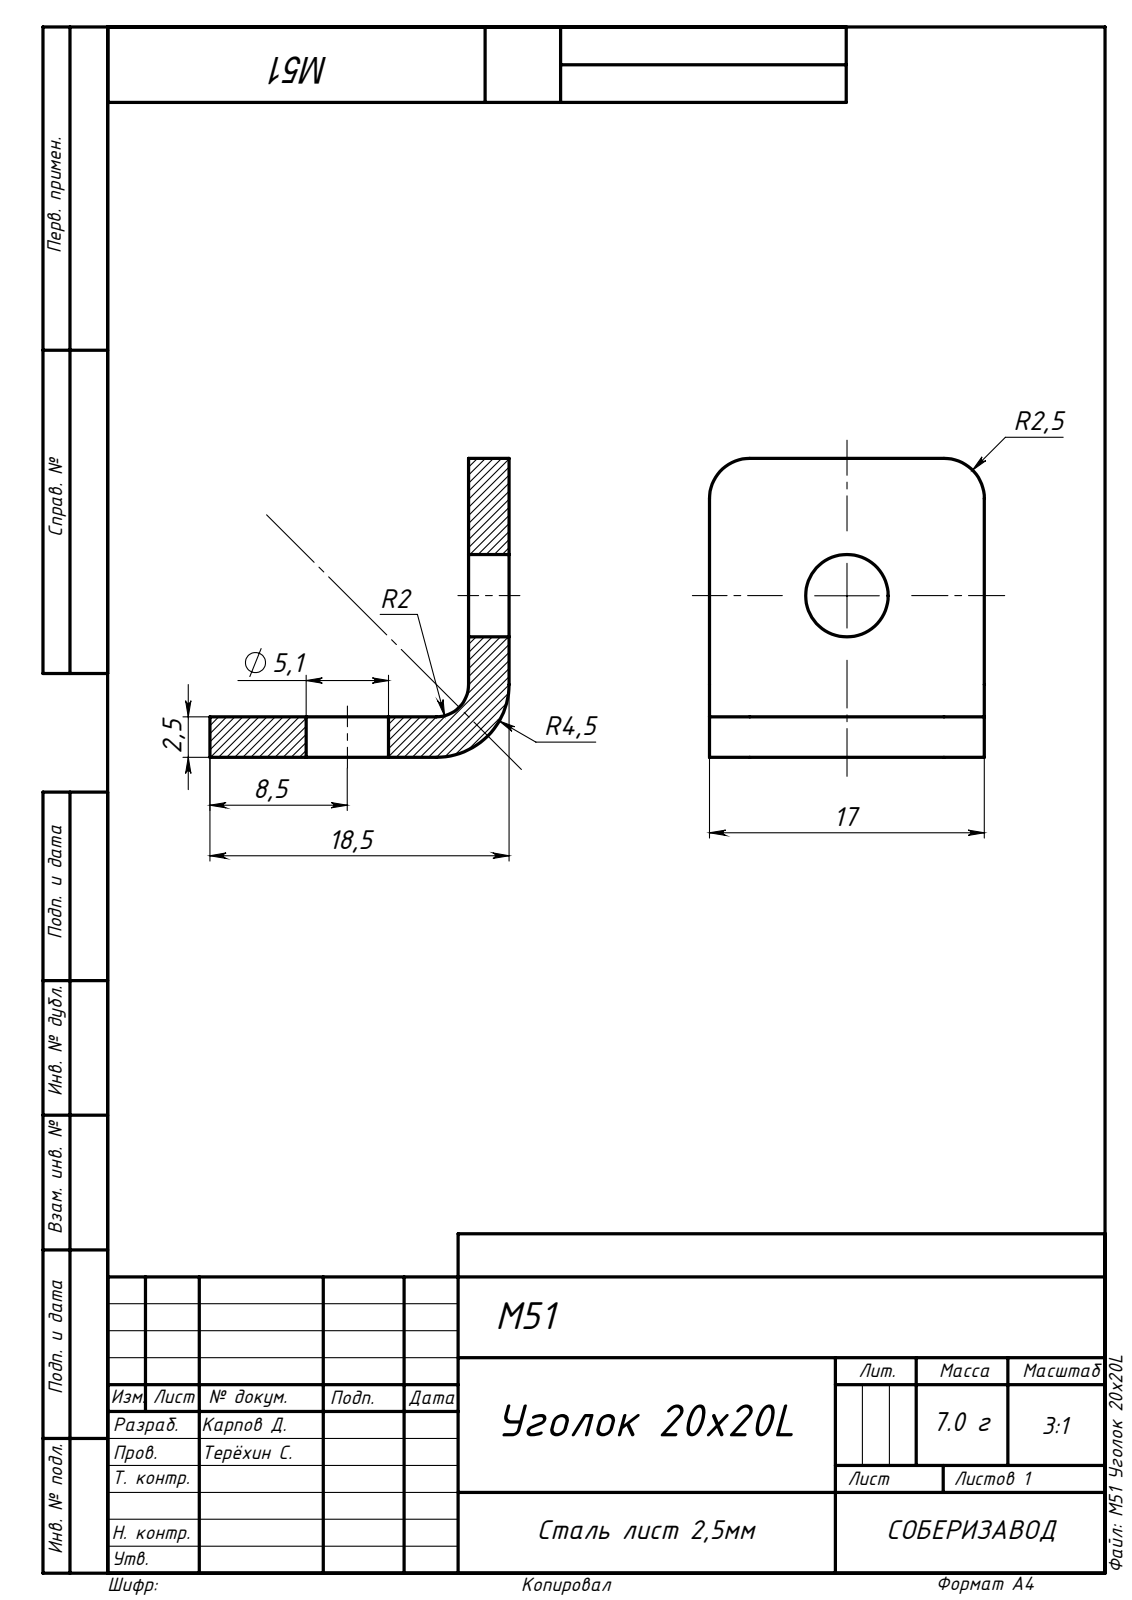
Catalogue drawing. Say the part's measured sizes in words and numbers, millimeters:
Its 3-D file was written by "SolidWorks 2021 (AUTOMOTIVE_DESIGN)". It is 1 solid with 22 faces: 12 planar, 10 cylindrical and 0 other. Overall it measures 18.5 by 18.5 by 17 millimeters. Its volume is 1 291 cubic millimeters and its surface area 1 353 square millimeters. Round holes: 2 of diameter 5.1. Partial cylindrical surfaces (rounded edges, fillets, slot ends): 4 of radius 2.5, 1 of radius 2, 1 of radius 4.5. The main face-to-face distances are 2.5, 17, 18.5, 16.
